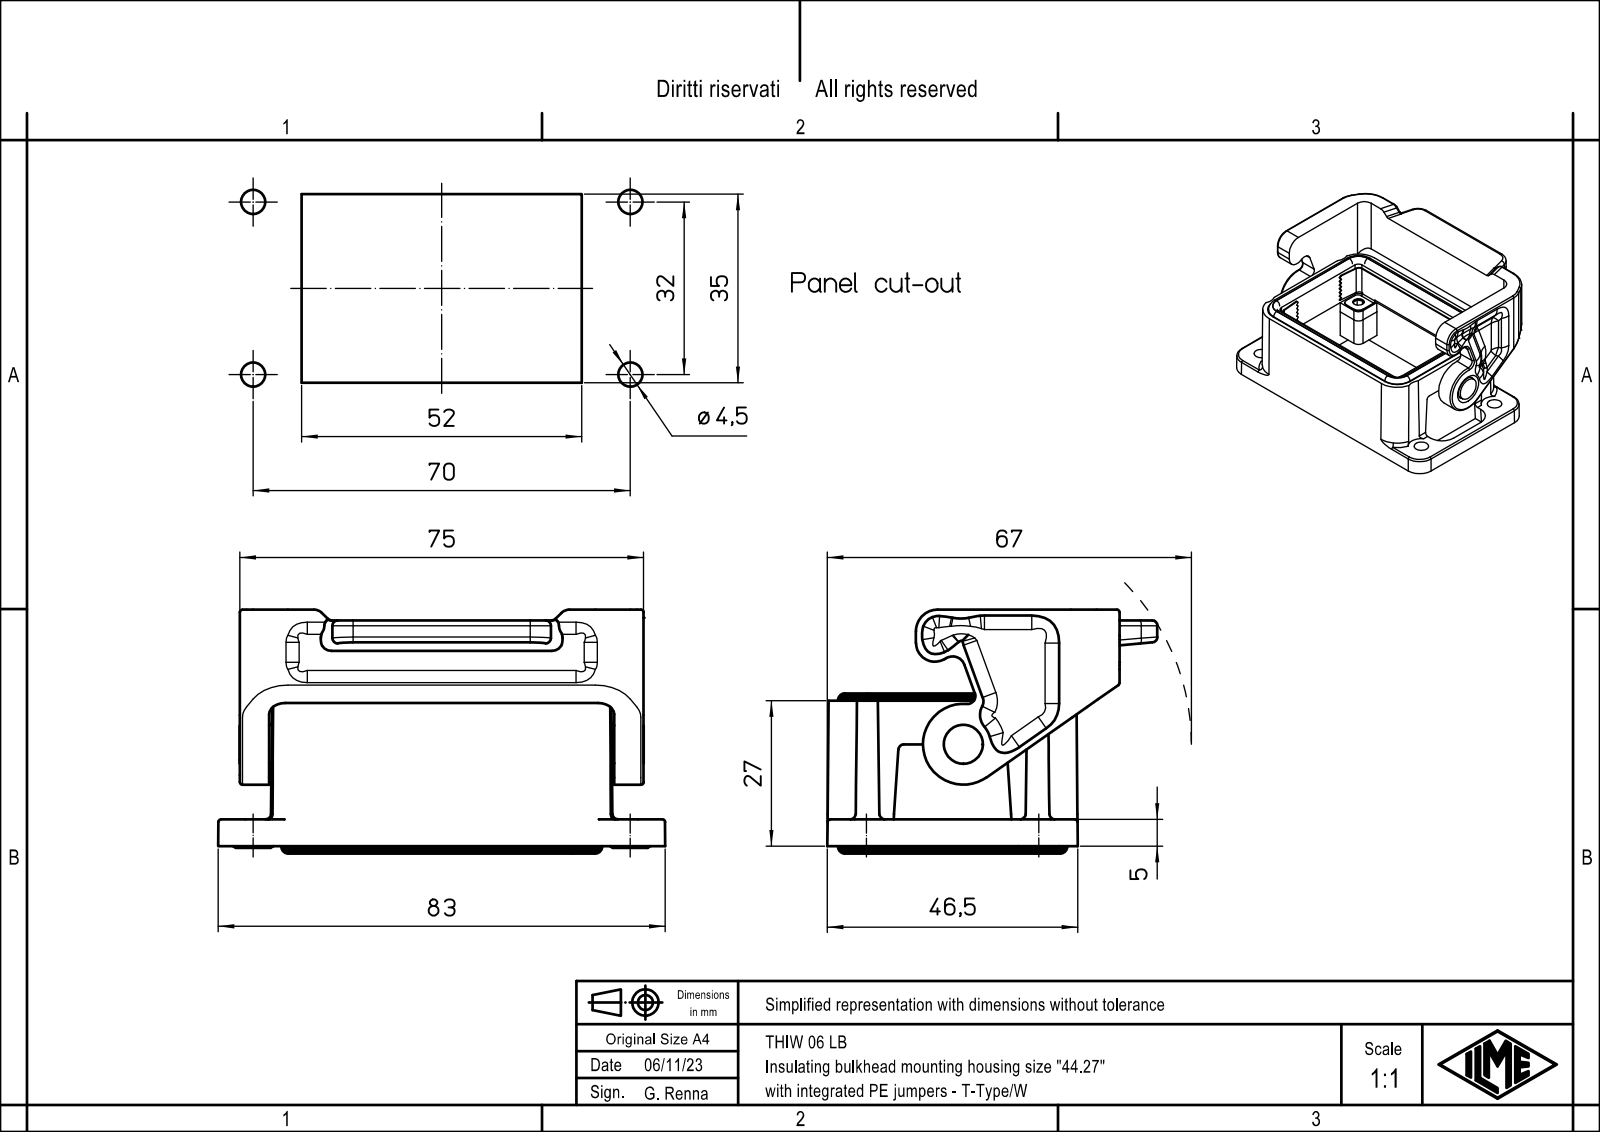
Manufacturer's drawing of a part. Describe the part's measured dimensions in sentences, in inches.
The part is named "THIW 06 LB". Its 3-D file was written by "Creo Elements/Direct Modeling 20.1B 02-Apr-2019 (C) Parametric Technology GmbH (AUTOMOTIVE_DESIGN)". It is 1 solid with 819 faces: 410 planar, 229 cylindrical and 180 other. Overall it measures 3.268 by 2.411 by 1.781 inches. Its volume is 2.953 cubic inches and its surface area 51.03 square inches. Round holes: 4 of diameter 0.098, 4 of diameter 0.138, 4 of diameter 0.177, 4 of diameter 0.272. Round bosses or shafts: 4 of diameter 0.189, 1 of diameter 0.276. Partial cylindrical surfaces (rounded edges, fillets, slot ends): 36 of radius 0.051, 24 of radius 0.039, 19 of radius 0.059, 15 of radius 0.079, 12 of radius 0.106, 12 of radius 0.217, 10 of radius 0.197, 7 of radius 0.118. The main face-to-face distances are 0.22, 2.265, 1.343, 1.512, 0.079, 0.217, 2.736, 0.197, 2.52, 0.169. The hole center spacings are 0.521, 1.269, 2.246, 2.527, 1.063, 1.26, 1.732, 2.032.
